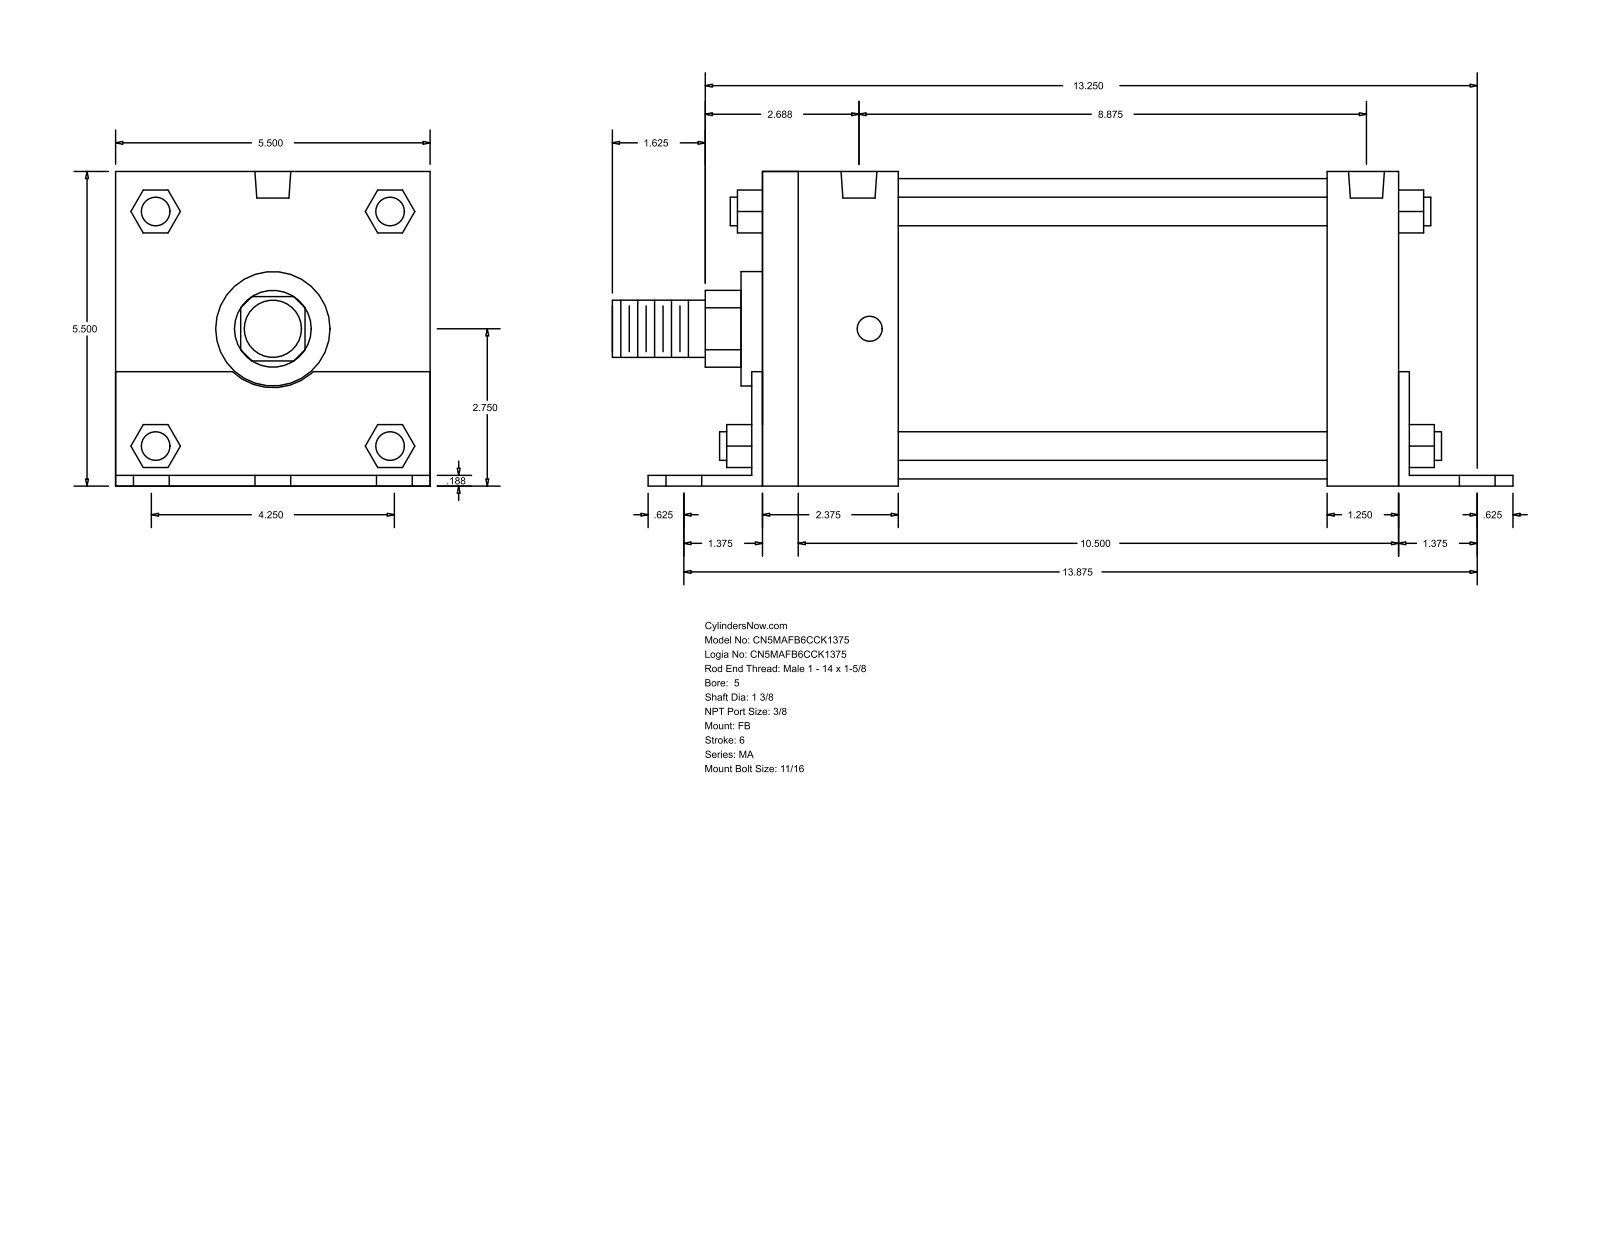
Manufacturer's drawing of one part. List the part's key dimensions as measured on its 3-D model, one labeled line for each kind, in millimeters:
Part name (STEP PRODUCT): MA_FB__0500_1.375
STEP written by: GSSL Pune (CONFIG_CONTROL_DESIGN)
Units: millimetres
Bodies: 0 solids, 140 faces (105 planar, 35 cylindrical, 0 other)
Overall size (bounding box): 400.05 × 139.75 × 139.7
Round holes (diameter × count): ⌀17.46 ×6, ⌀11.11 ×4, ⌀15.93 ×2
Round bosses / shafts (diameter × count): ⌀12.7 ×4, ⌀133.35 ×1, ⌀50.8 ×1, ⌀34.92 ×1, ⌀25.4 ×1
Partial cylindrical surfaces — rounded edges, fillets, slot ends (radius × count): R17.06 ×1, R26.16 ×1
Main face-to-face distances: 139.7, 4.76, 139.75, 287.34, 4.71, 134.99, 282.58, 292.1, 31.75, 36.51
Hole centre spacings: 53.98, 356.54, 352.43, 73.04, 76.33, 94.68, 98.64, 107.96
